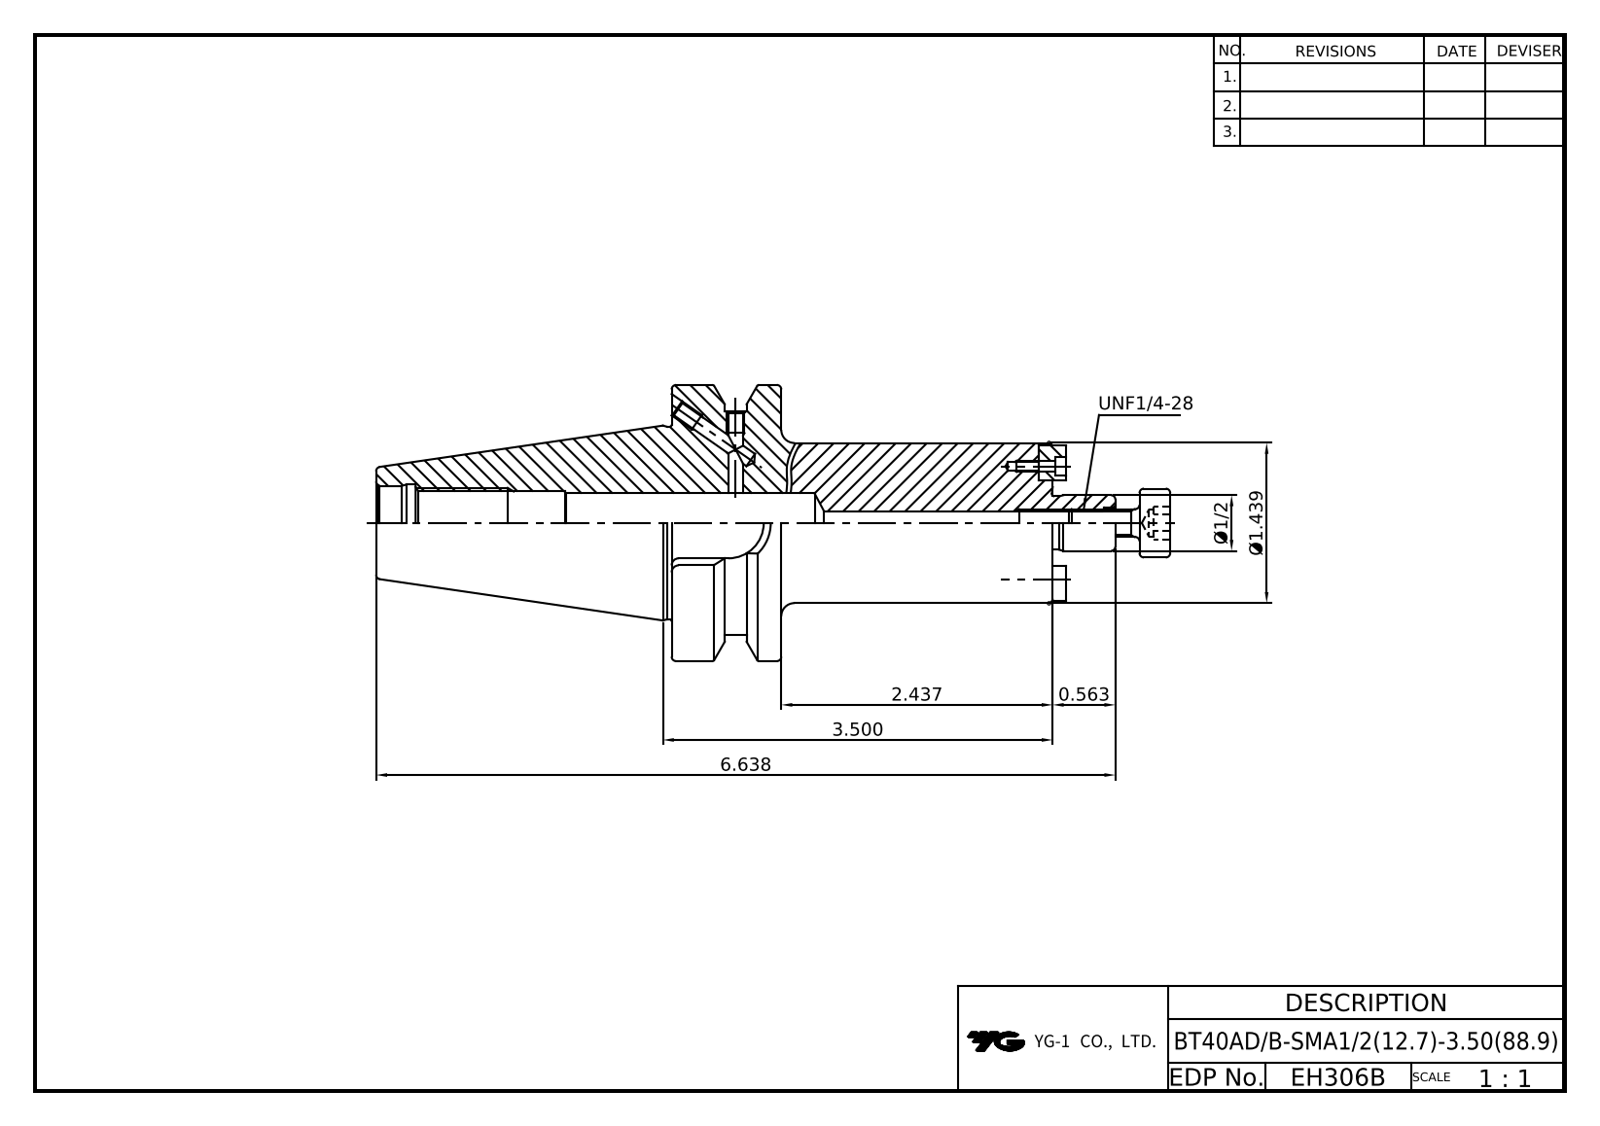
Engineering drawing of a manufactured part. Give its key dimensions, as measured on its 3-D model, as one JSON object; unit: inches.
{"part_name": "LO-BT40ADB-SMA12.7-88.9; DRIVE KEY-6.35x6.35x8; HEX'' WRENCH BOLT-UNC#3-48x1_4L; COLLAR BOLT-UNF1_4-28x16L", "step_written_by": "Autodesk Inventor 2026 (AUTOMOTIVE_DESIGN)", "units": "inches", "bodies": {"solids": 6, "faces": 147, "planar": 72, "cylindrical": 44, "other": 31}, "overall_size": [7.11, 2.48, 2.48], "volume_in3": 11.26, "surface_area_in2": 53.8, "round_holes": [[0.128, 4], [0.157, 4], [0.076, 2], [0.102, 2], [0.165, 2], [0.211, 1], [0.25, 1], [0.276, 1], [0.545, 1], [0.669, 1], [0.693, 1]], "round_bosses_or_shafts": [[0.161, 2], [0.099, 2], [2.48, 1], [2.071, 1], [1.732, 1], [1.439, 1], [0.618, 1], [0.5, 1]], "partial_cylinders_radius": [[0.125, 2], [0.317, 1]], "face_to_face_distances": [0.984, 3.421, 2.437, 1.78, 0.197, 0.634, 3.508, 0.126, 3.295, 2.311], "hole_center_spacings": [0.51, 1.02]}
